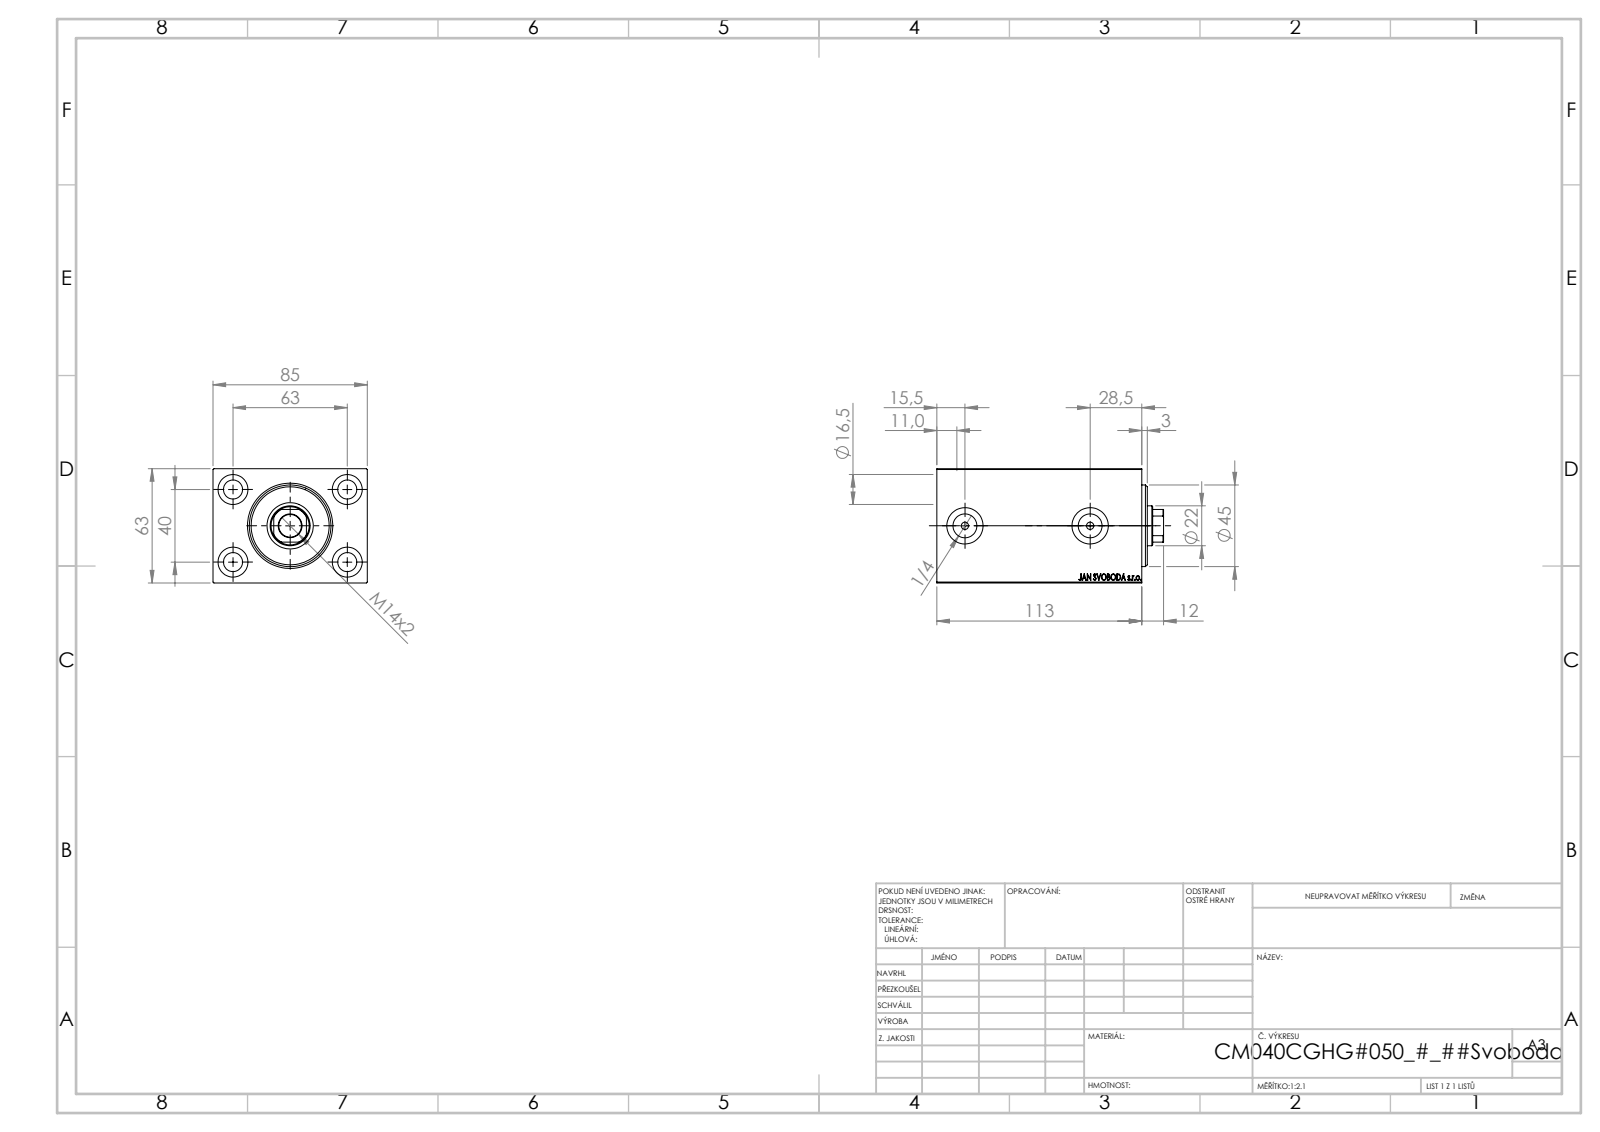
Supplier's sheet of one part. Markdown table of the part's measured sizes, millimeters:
| quantity | value |
| --- | --- |
| part name | V450CM_VC_B; V450CM_C_Body; V450CM_C_VCP |
| STEP written by | SolidWorks 2019 (CONFIG_CONTROL_DESIGN) |
| units | millimeters |
| bodies | 3 solids, 862 faces (408 planar, 60 cylindrical, 394 other) |
| overall size | 125 × 85 × 63 |
| volume | 511 957 mm³ |
| surface area | 92 730 mm² |
| round holes (diameter × count) | 10.5 × 4, 16.5 × 4, 4 × 2, 13.16 × 2, 20 × 2, 12.5 × 1, 22 × 1, 25.5 × 1, 40 × 1, 42 × 1, 45 × 1 |
| partial cylindrical surfaces (radius × count) | 10.5 × 1 |
| main face-to-face distances | 63, 85, 12, 101, 113, 51, 89, 11, 102, 1 |
| hole center spacings | 37.31, 40, 63, 74.63, 69 |
